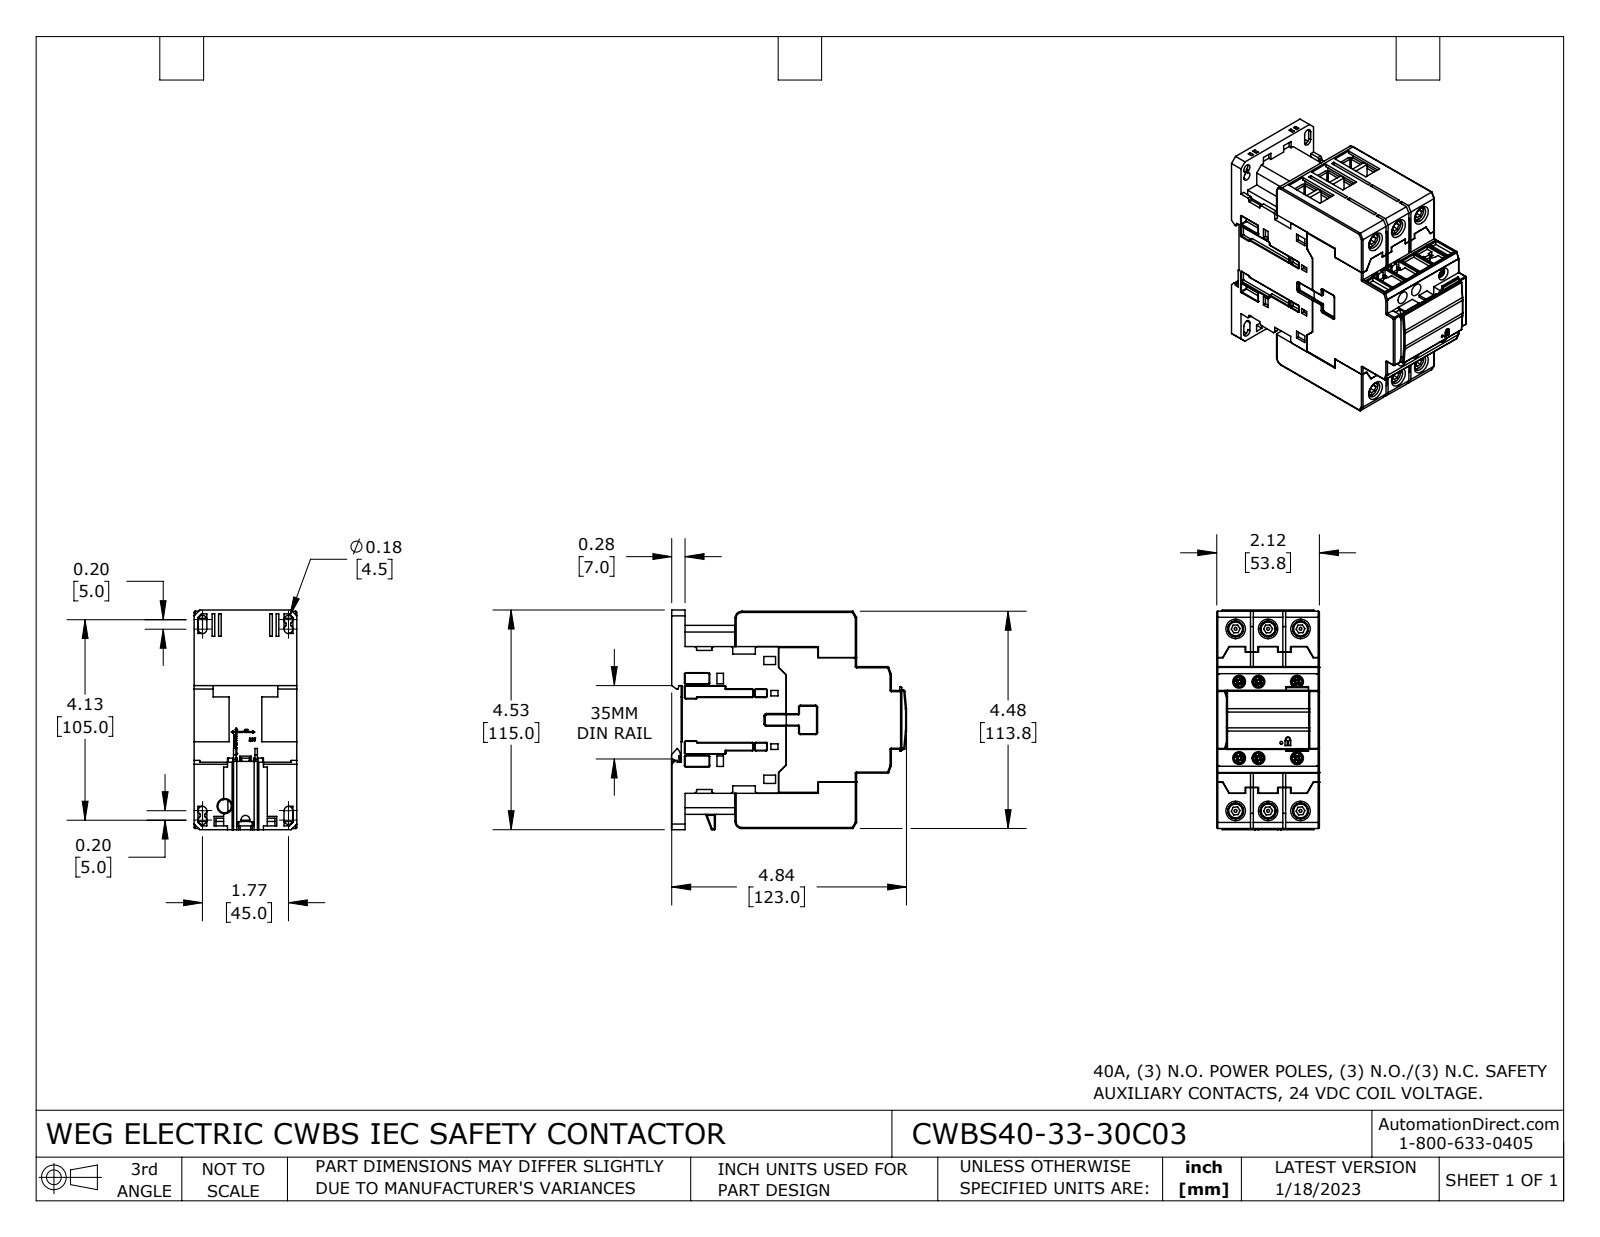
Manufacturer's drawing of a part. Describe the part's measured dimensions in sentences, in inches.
The part is named "CWBS40-33-30C03". Its 3-D file was written by "SolidWorks 2021 (CONFIG_CONTROL_DESIGN)". It is 37 solids with 2637 faces: 1669 planar, 550 cylindrical and 418 other. Overall it measures 4.846 by 4.528 by 2.118 inches. Its volume is 33.67 cubic inches and its surface area 209.3 square inches. Round holes: 6 of diameter 0.124, 6 of diameter 0.197, 6 of diameter 0.264, 6 of diameter 0.323, 4 of diameter 0.177, 2 of diameter 0.125, 2 of diameter 0.276, 1 of diameter 0.059. Round bosses or shafts: 6 of diameter 0.343, 6 of diameter 0.236, 6 of diameter 0.135. Partial cylindrical surfaces (rounded edges, fillets, slot ends): 89 of radius 0.02, 69 of radius 0.012, 48 of radius 0.004, 42 of radius 0.024, 18 of radius 0.079, 5 of radius 0.089, 3 of radius 0.039, 3 of radius 0.059. The main face-to-face distances are 0.059, 2.118, 0.669, 0.728, 3.024, 3.752, 0.108, 0.217, 3.811, 0.098. The hole center spacings are 0.669, 1.091, 1.241, 1.669, 2.665, 2.73, 2.949, 3.811.
